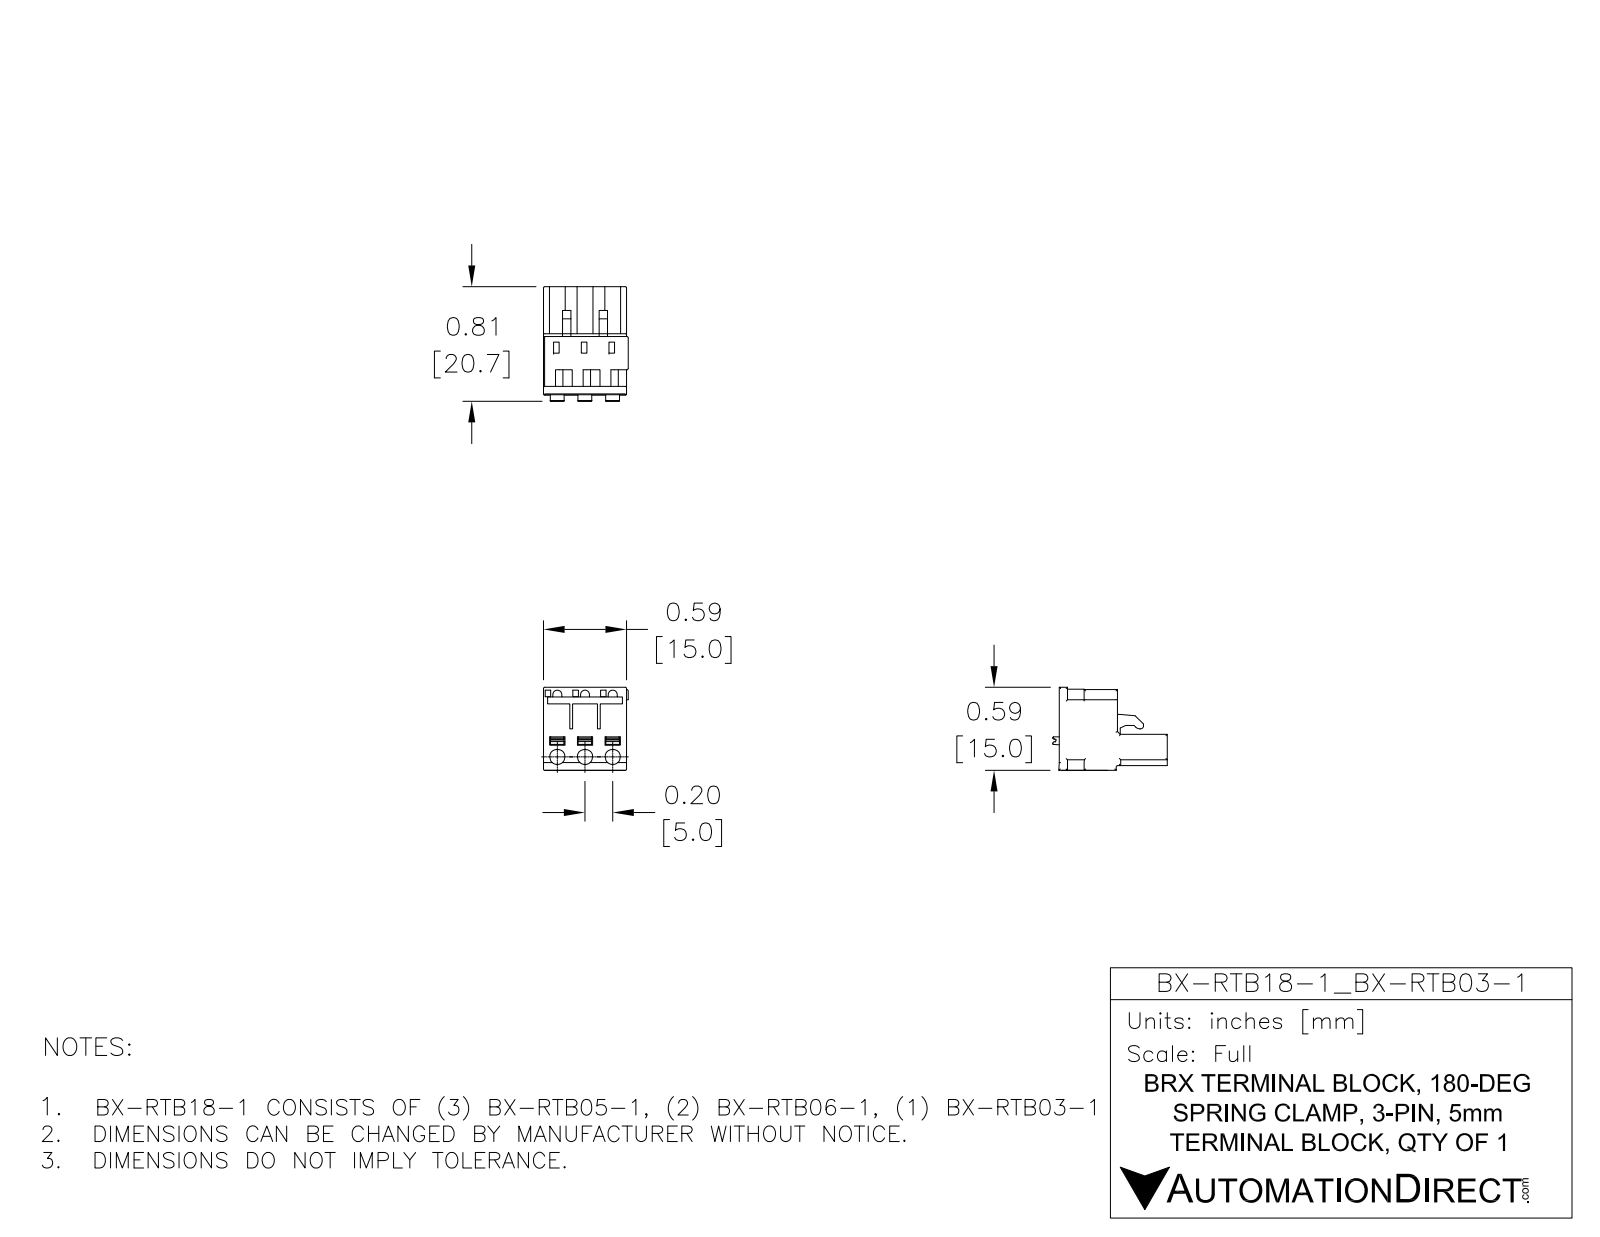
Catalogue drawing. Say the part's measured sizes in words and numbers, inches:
The part is named "BX-RTB18-1". Its 3-D file was written by "SolidWorks 2017 (AUTOMOTIVE_DESIGN)". It is 8 solids with 3924 faces: 2028 planar, 1224 cylindrical and 672 other. Overall it measures 8.417 by 0.815 by 0.591 inches. Its volume is 1.637 cubic inches and its surface area 32.14 square inches. Round holes: 30 of diameter 0.063, 30 of diameter 0.108, 30 of diameter 0.124. Partial cylindrical surfaces (rounded edges, fillets, slot ends): 360 of radius 0.004, 213 of radius 0.01, 30 of radius 0.032, 30 of radius 0.039, 30 of radius 0.095, 30 of radius 0.099, 4 of radius 0.008, 1 of radius 0.011. The main face-to-face distances are 0.574, 1.484, 0.224, 0.35, 0.413, 0.5, 0.354, 0.591, 2.969, 0.256. The hole center spacings are 0.197, 0.2, 0.394, 0.396, 0.037, 0.591, 0.592, 1.681.
